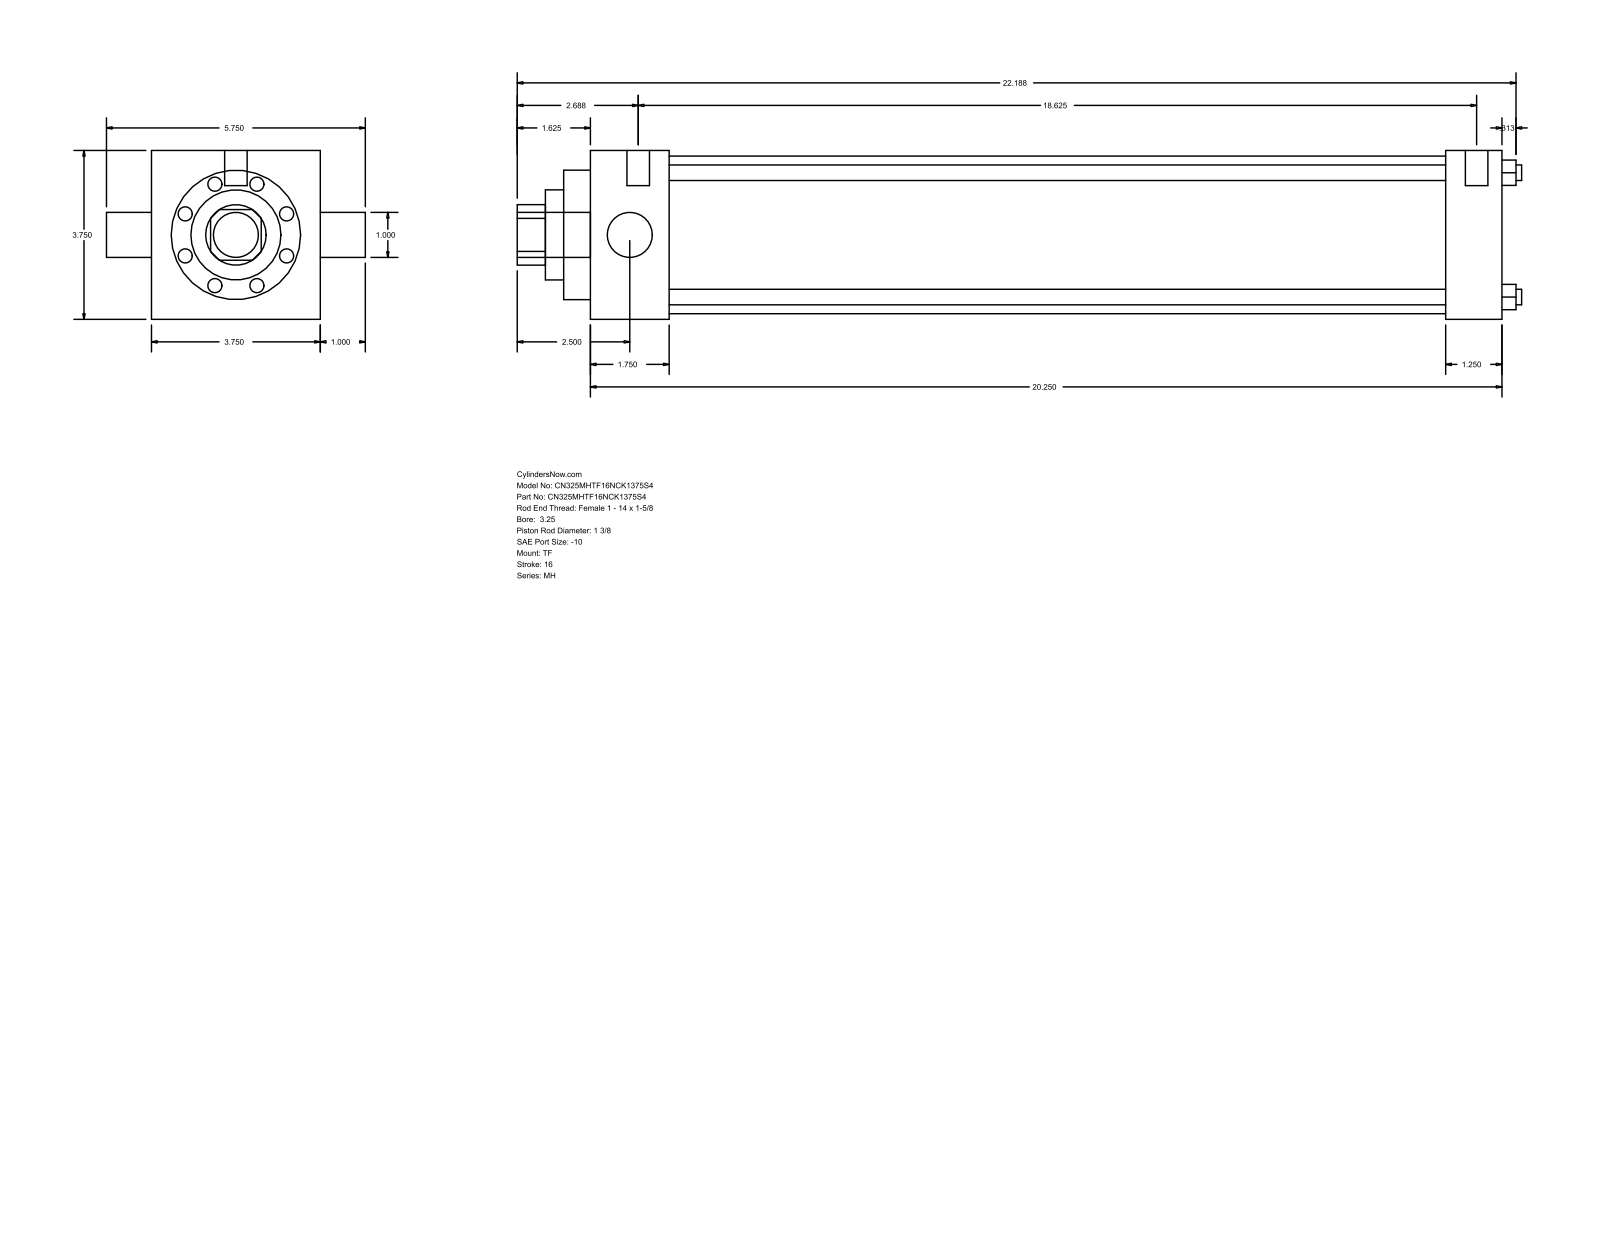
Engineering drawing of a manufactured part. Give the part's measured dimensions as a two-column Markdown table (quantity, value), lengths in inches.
| quantity | value |
| --- | --- |
| part name | MH_TF__0325_1.375 |
| STEP written by | GSSL Pune (CONFIG_CONTROL_DESIGN) |
| units | inches |
| bodies | 0 solids, 86 faces (61 planar, 25 cylindrical, 0 other) |
| overall size | 22.313 × 5.75 × 3.75 |
| round holes (diameter × count) | 0.345 × 4, 1 × 1, 1.375 × 1, 2 × 1, 2.875 × 1, 3.5 × 1 |
| round bosses / shafts (diameter × count) | 0.219 × 3, 0.5 × 2, 1 × 1 |
| partial cylindrical surfaces (radius × count) | 0.672 × 1 |
| main face-to-face distances | 3.75, 20.25, 1.75, 19, 17.25, 18.5, 1.25, 0.594, 2.344, 19.594 |
| hole center spacings | 1.952, 2.76, 3.903 |
